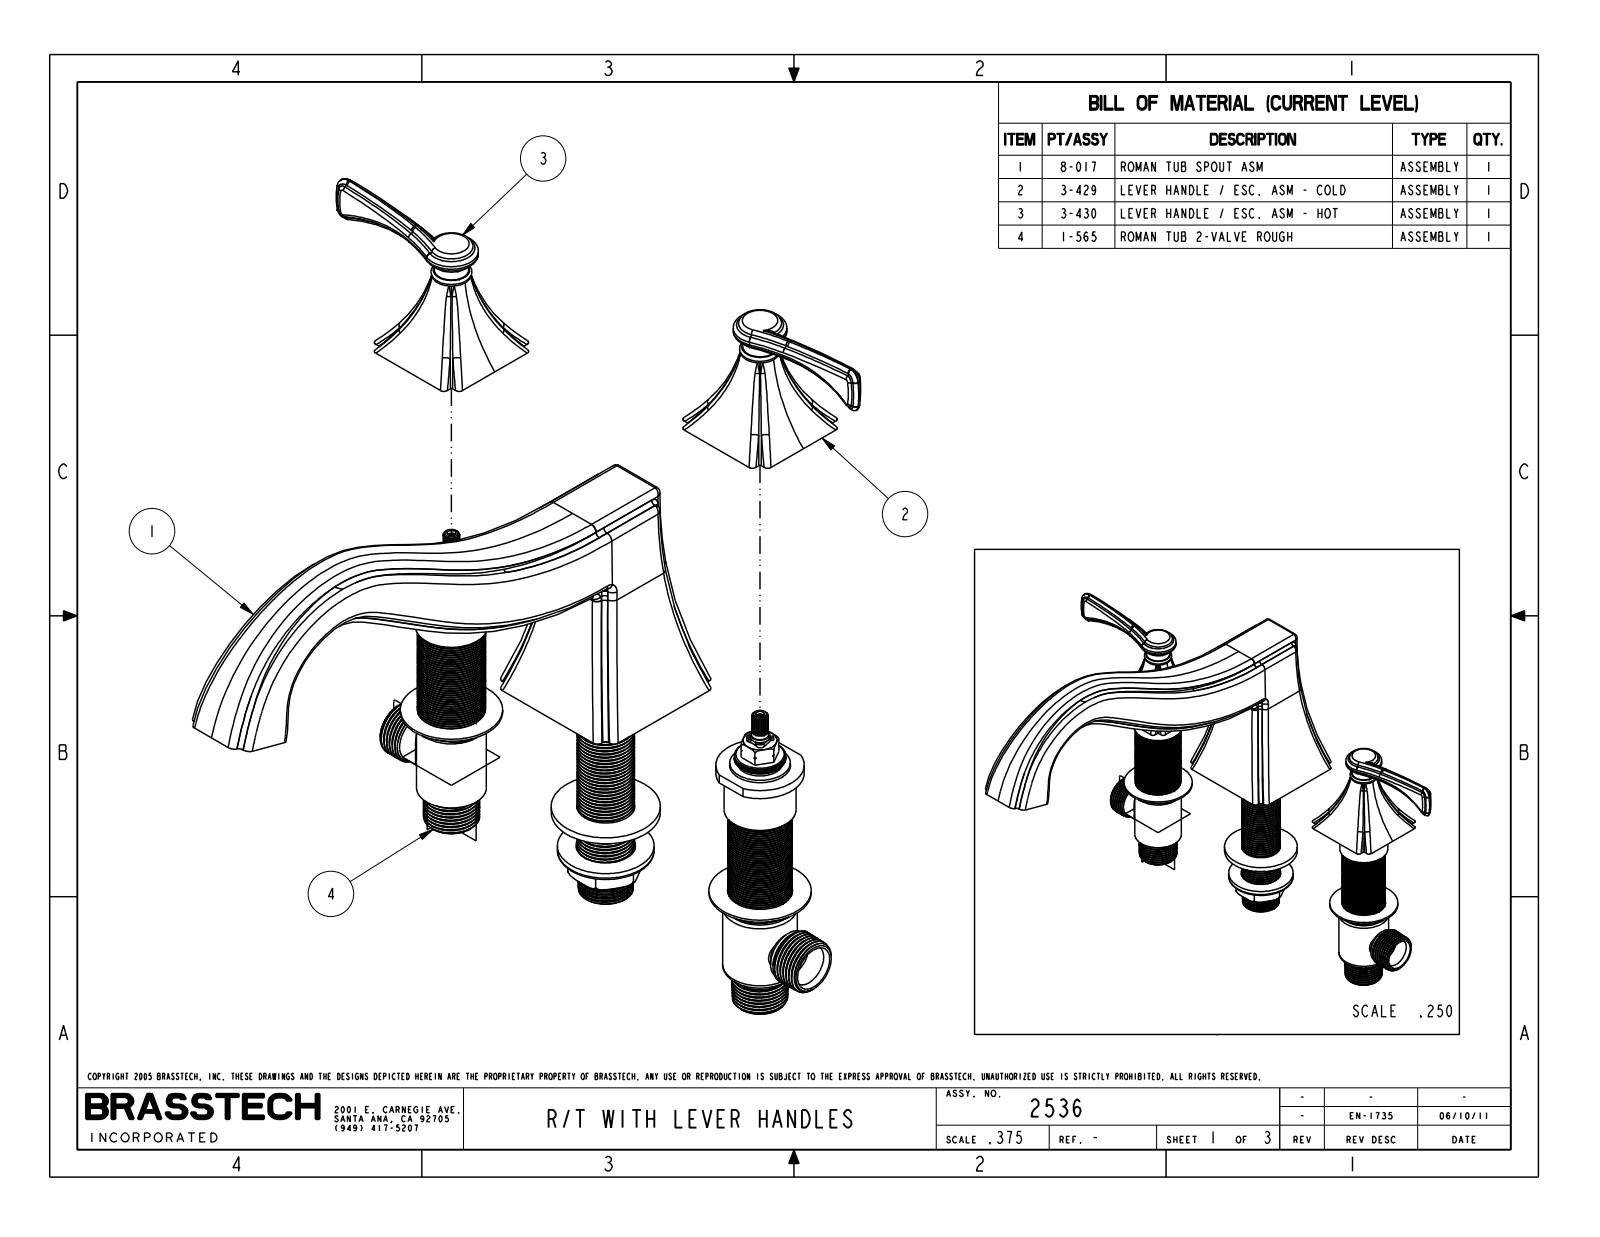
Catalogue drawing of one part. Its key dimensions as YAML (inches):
part_name: "2536_WEB"
step_written_by: "PRO/ENGINEER BY PARAMETRIC TECHNOLOGY CORPORATION, 2009300 (CONFIG_CONTROL_DESIGN)"
units: inches
bodies: {solids: 0, faces: 405, planar: 12, cylindrical: 39, other: 354}
overall_size: [13.526, 11.725, 6.178]
round_bosses_or_shafts:
  - {diameter: 0.63, count: 2}
partial_cylinders:
  - {radius: 0.118, count: 4}
  - {radius: 0.08, count: 3}
  - {radius: 0.04, count: 2}
  - {radius: 0.492, count: 2}
  - {radius: 3.863, count: 2}
  - {radius: 4.112, count: 2}
  - {radius: 4.195, count: 2}
  - {radius: 10.5, count: 2}
face_to_face_distances: [4.26, 4.25, 1.922, 1.912, 2.338, 2.316, 2.306, 0.394, 1.944, 1.726]
